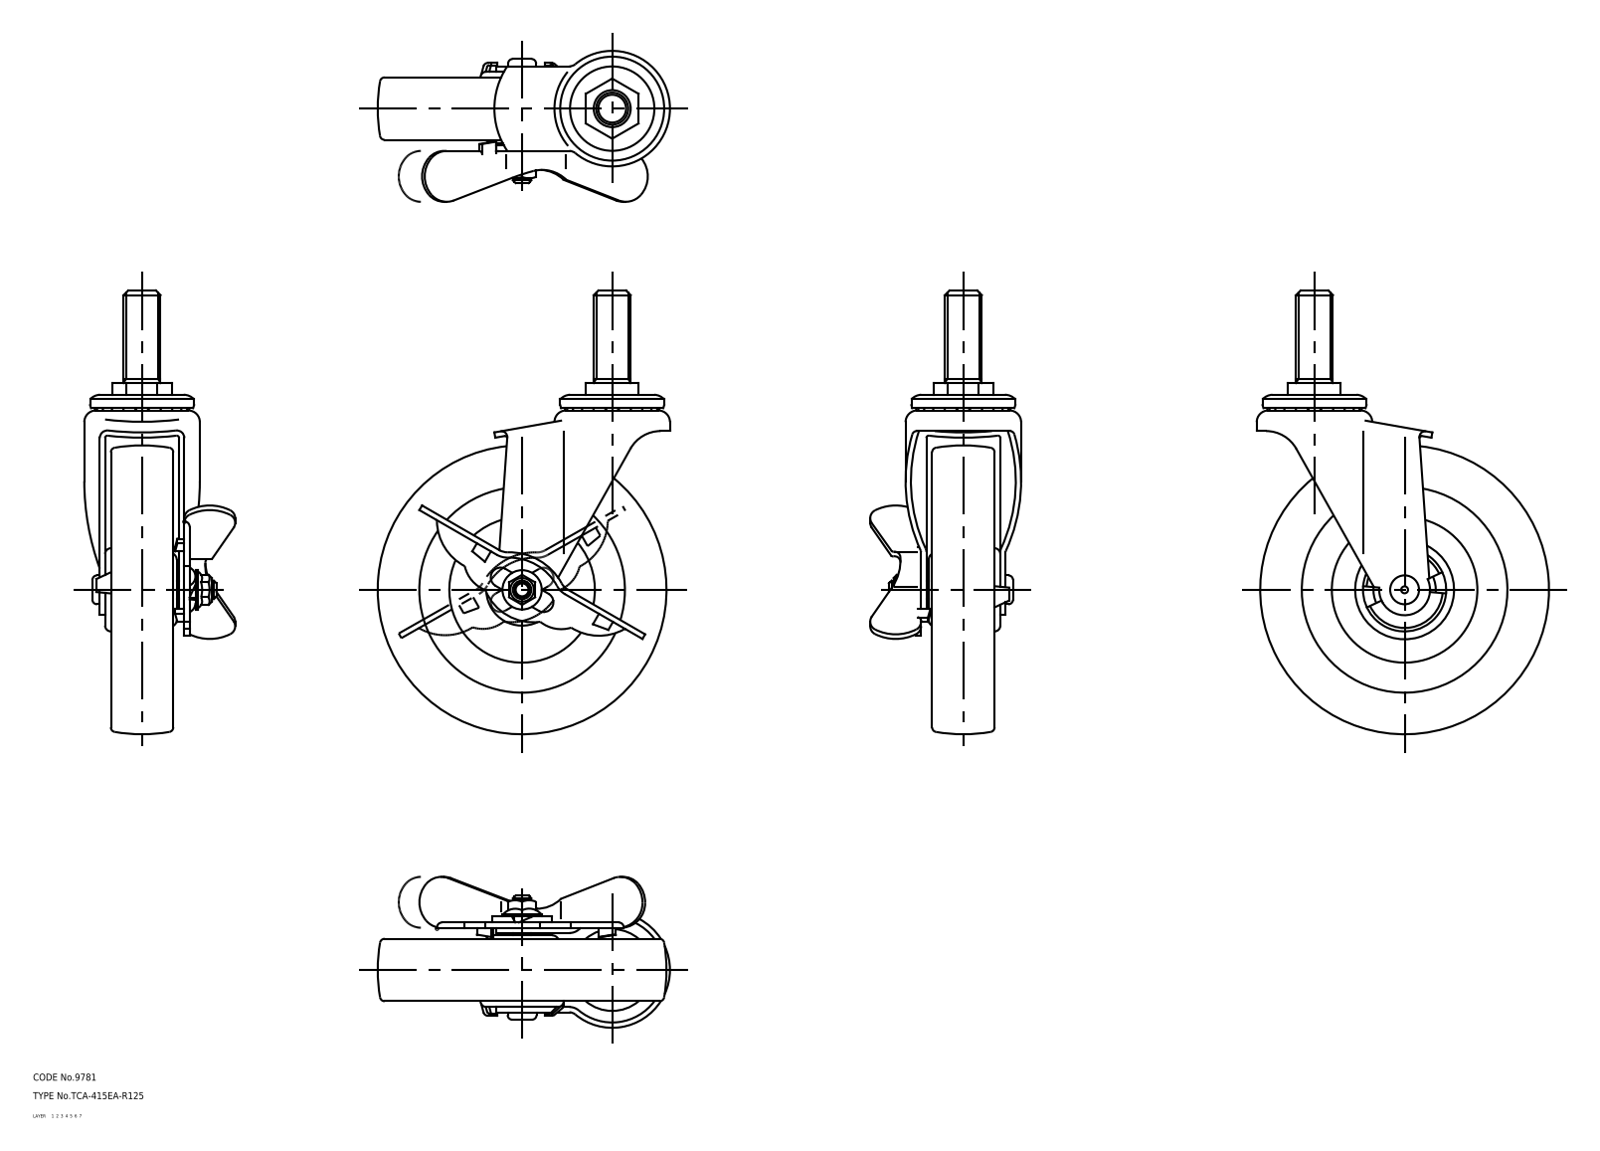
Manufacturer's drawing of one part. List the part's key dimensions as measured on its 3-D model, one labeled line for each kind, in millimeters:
Part name (STEP PRODUCT): wheel; mounting plate; main shaft; lever (+2 more)
STEP written by: CADfix (AUTOMOTIVE_DESIGN)
Units: millimetres
Bodies: 6 solids, 329 faces (0 planar, 0 cylindrical, 329 other)
Overall size (bounding box): 192 × 126.5 × 65.3
Volume: 372 839 mm³ · Surface area: 76 175 mm²
